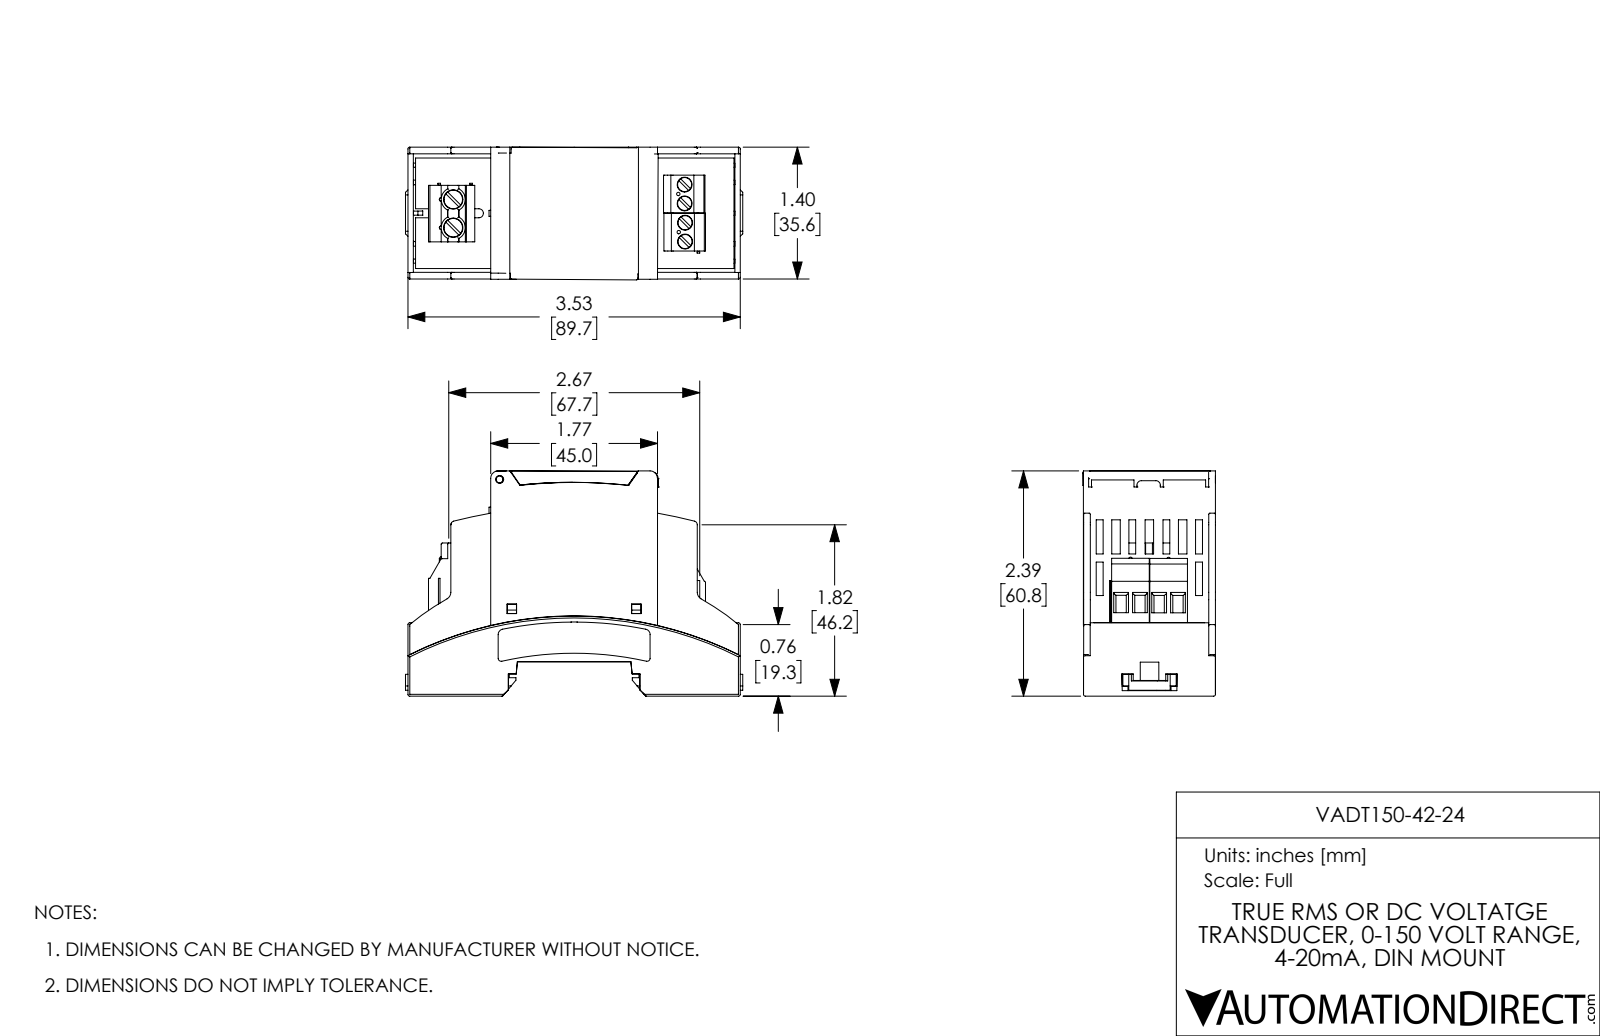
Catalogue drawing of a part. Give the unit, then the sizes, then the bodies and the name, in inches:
Units: inches
Overall size (bounding box): 4.203 × 2.298 × 1.46
Round holes (diameter × count): ⌀0.157 ×4, ⌀0.205 ×2
Round bosses / shafts (diameter × count): ⌀0.051 ×6, ⌀0.15 ×4, ⌀0.018 ×3, ⌀0.197 ×2
Partial cylindrical surfaces — rounded edges, fillets, slot ends (radius × count): R0.006 ×27, R0.039 ×12, R0.02 ×11, R0.008 ×10, R0.026 ×8, R0.012 ×6, R0.032 ×4, R0.04 ×4
Main face-to-face distances: 1.435, 0.064, 0.437, 0.501, 1.279, 1.249, 0.266, 0.703, 0.767, 0.771
Hole centre spacings: 0.2, 0.4, 2.467, 0.375, 0.6, 2.468, 2.469, 2.482
Volume: 3.182 in³ · Surface area: 78.38 in²
Bodies: 7 solids, 895 faces (538 planar, 166 cylindrical, 191 other)
Part name (STEP PRODUCT): VADT150-42-24
STEP written by: SolidWorks 2021 (AUTOMOTIVE_DESIGN)
